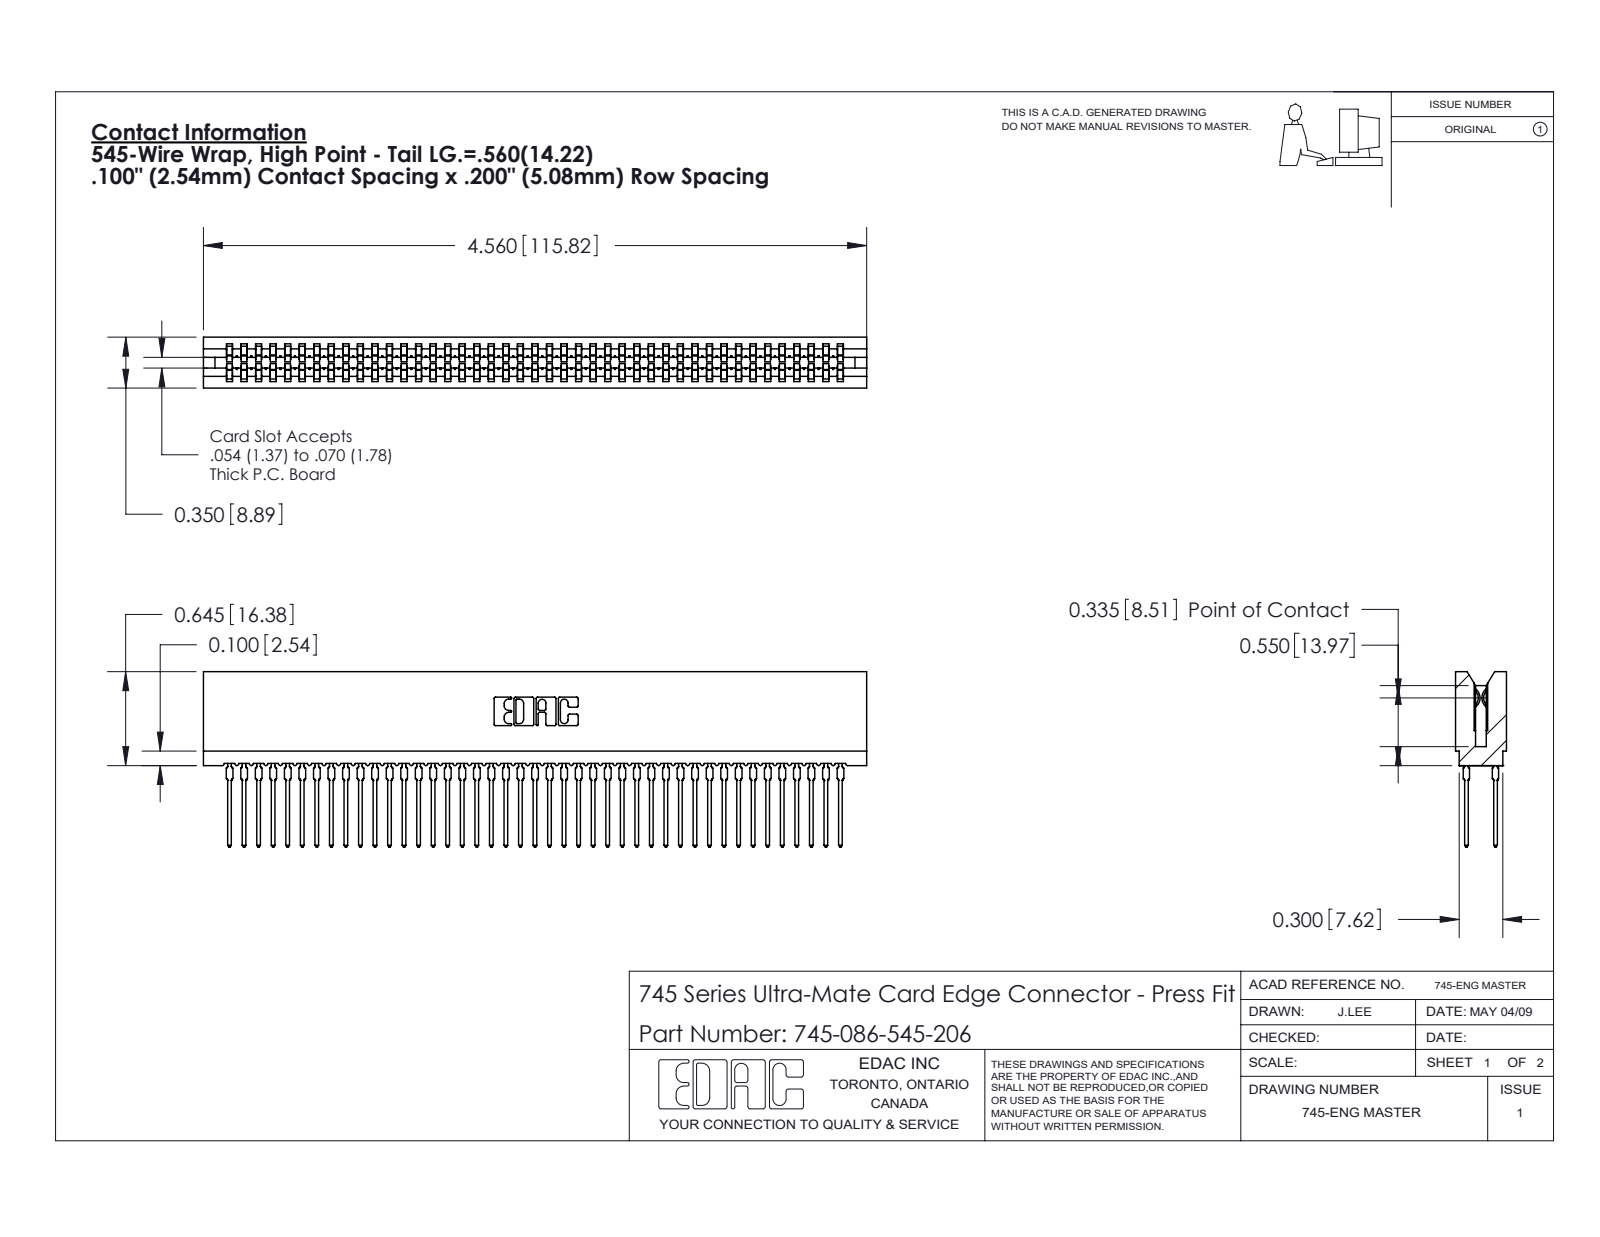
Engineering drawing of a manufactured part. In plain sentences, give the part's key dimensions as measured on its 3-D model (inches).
The part is named "745-292-001_545; 745-086-545-206; 745 Part_Insulator Option - 06". Its 3-D file was written by "SolidWorks 2020 (CONFIG_CONTROL_DESIGN)". It is 87 solids with 7793 faces: 4012 planar, 1545 cylindrical and 2236 other. Overall it measures 4.56 by 1.206 by 0.35 inches. Its volume is 0.653 cubic inches and its surface area 35.84 square inches. Partial cylindrical surfaces (rounded edges, fillets, slot ends): 172 of radius 0.021, 86 of radius 0.015, 22 of radius 0.01, 8 of radius 0.005, 8 of radius 0.011, 6 of radius 0.007, 6 of radius 0.031, 3 of radius 0.026. The main face-to-face distances are 0.063, 0.287, 0.2, 0.35, 0.045, 0.305, 0.018, 0.243, 0.138, 0.212.
